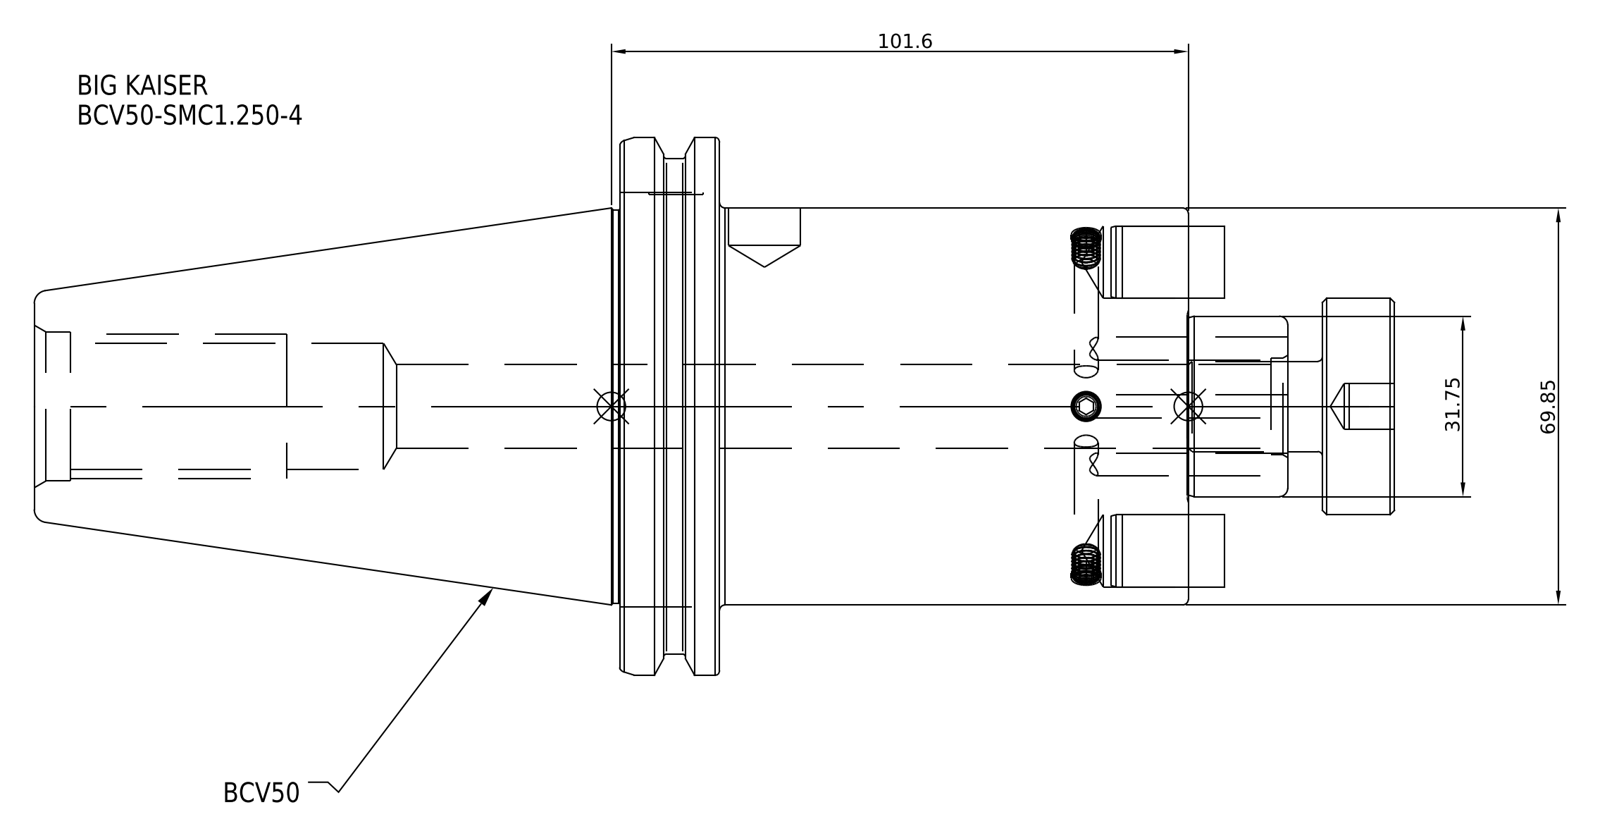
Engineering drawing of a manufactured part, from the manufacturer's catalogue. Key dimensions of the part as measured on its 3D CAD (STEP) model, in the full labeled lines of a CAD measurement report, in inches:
Part name (STEP PRODUCT): BCV50-SMC1_250-4
STEP written by: SolidWorks 2021 (CONFIG_CONTROL_DESIGN)
Units: inches
Bodies: 1 solid, 35 faces (17 planar, 12 cylindrical, 6 other)
Overall size (bounding box): 8.252 × 3.875 × 3.875
Volume: 42.01 in³ · Surface area: 91.93 in²
Round holes (diameter × count): ⌀0.578 ×1
Round bosses / shafts (diameter × count): ⌀3.875 ×1, ⌀3.594 ×1, ⌀2.75 ×1
Main face-to-face distances: 0.691, 3.25, 3.941, 8, 4.75, 4.059, 0.5, 0.252, 3.502, 4.193
